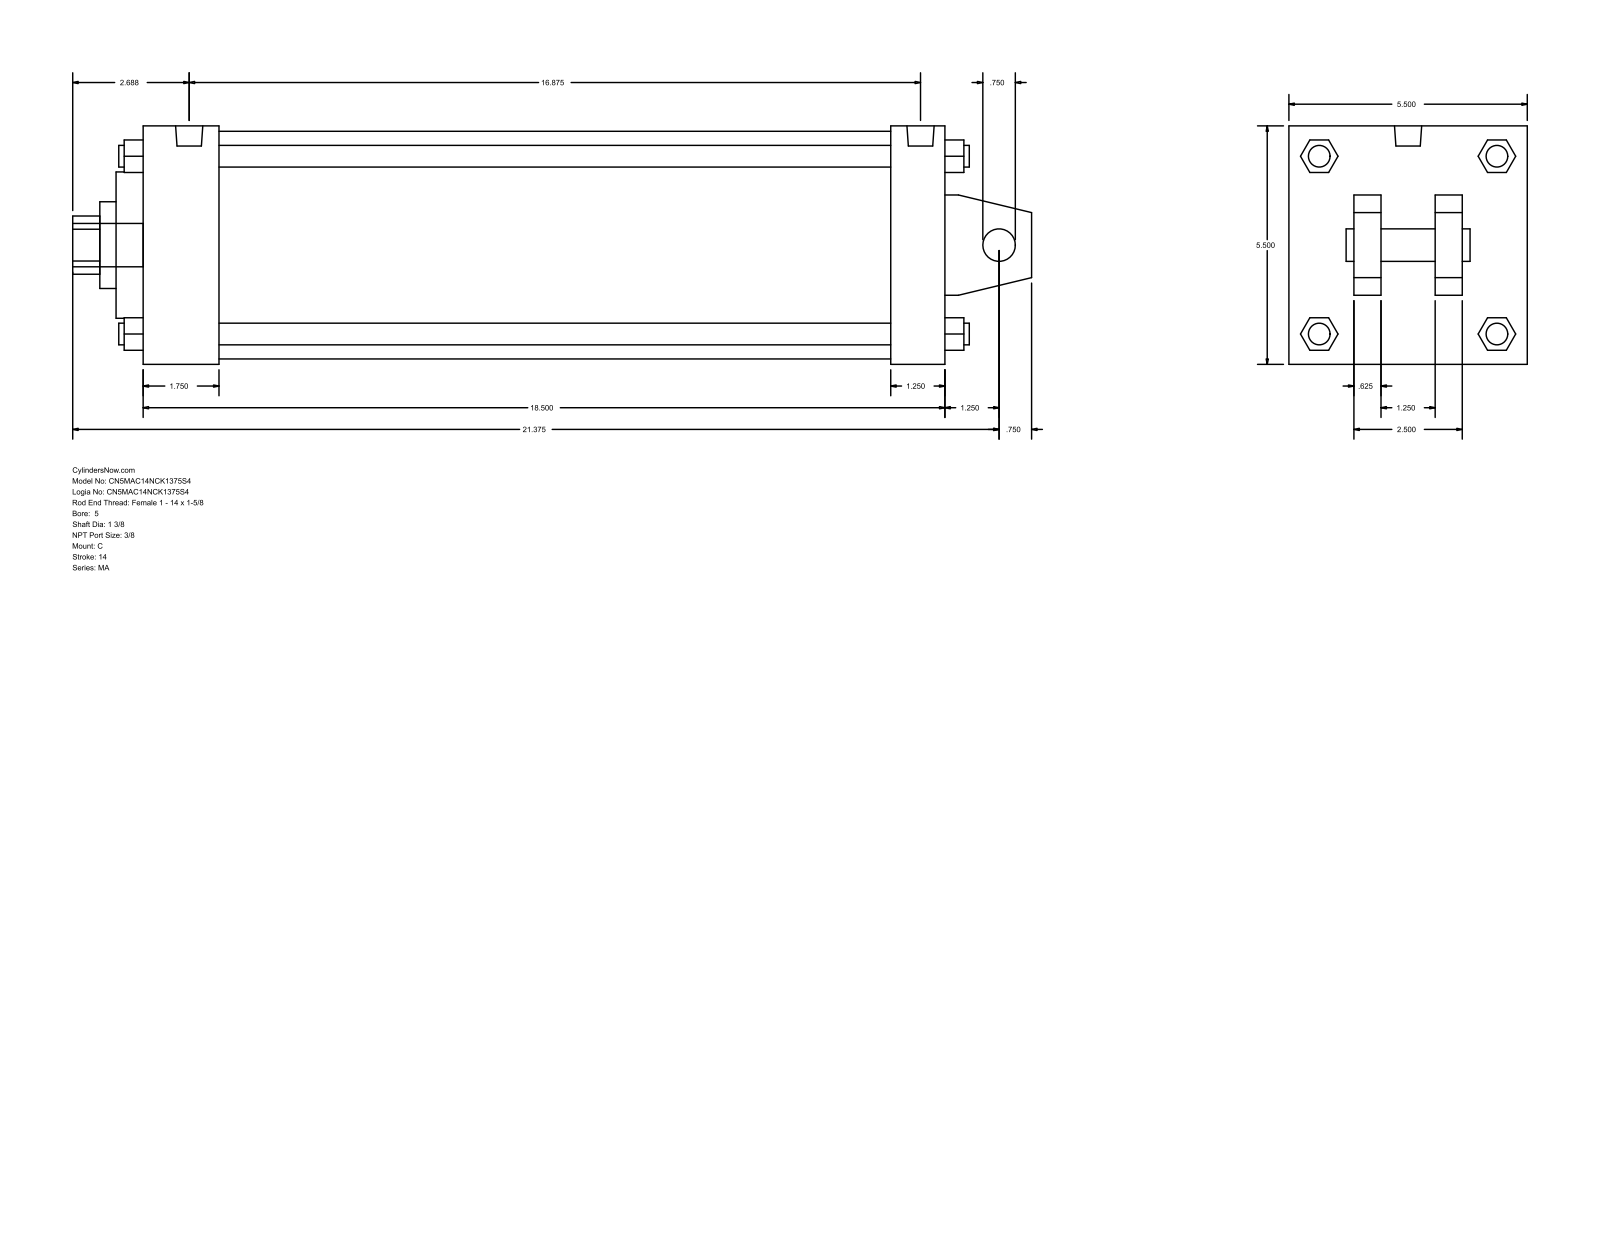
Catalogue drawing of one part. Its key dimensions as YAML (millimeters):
part_name: "MA_C__0500_1.375"
step_written_by: "GSSL Pune (CONFIG_CONTROL_DESIGN)"
units: millimeters
bodies: {solids: 0, faces: 141, planar: 109, cylindrical: 32, other: 0}
overall_size: [561.98, 139.7, 139.7]
round_holes:
  - {diameter: 19.05, count: 1}
  - {diameter: 34.92, count: 1}
  - {diameter: 50.8, count: 1}
  - {diameter: 85.72, count: 1}
  - {diameter: 133.35, count: 1}
round_bosses_or_shafts:
  - {diameter: 12.7, count: 4}
  - {diameter: 11.11, count: 4}
  - {diameter: 15.93, count: 2}
  - {diameter: 25.4, count: 1}
partial_cylinders:
  - {radius: 17.06, count: 1}
face_to_face_distances: [139.7, 469.91, 15.87, 438.16, 31.75, 44.45, 393.71, 425.46, 38.1, 101.6]
